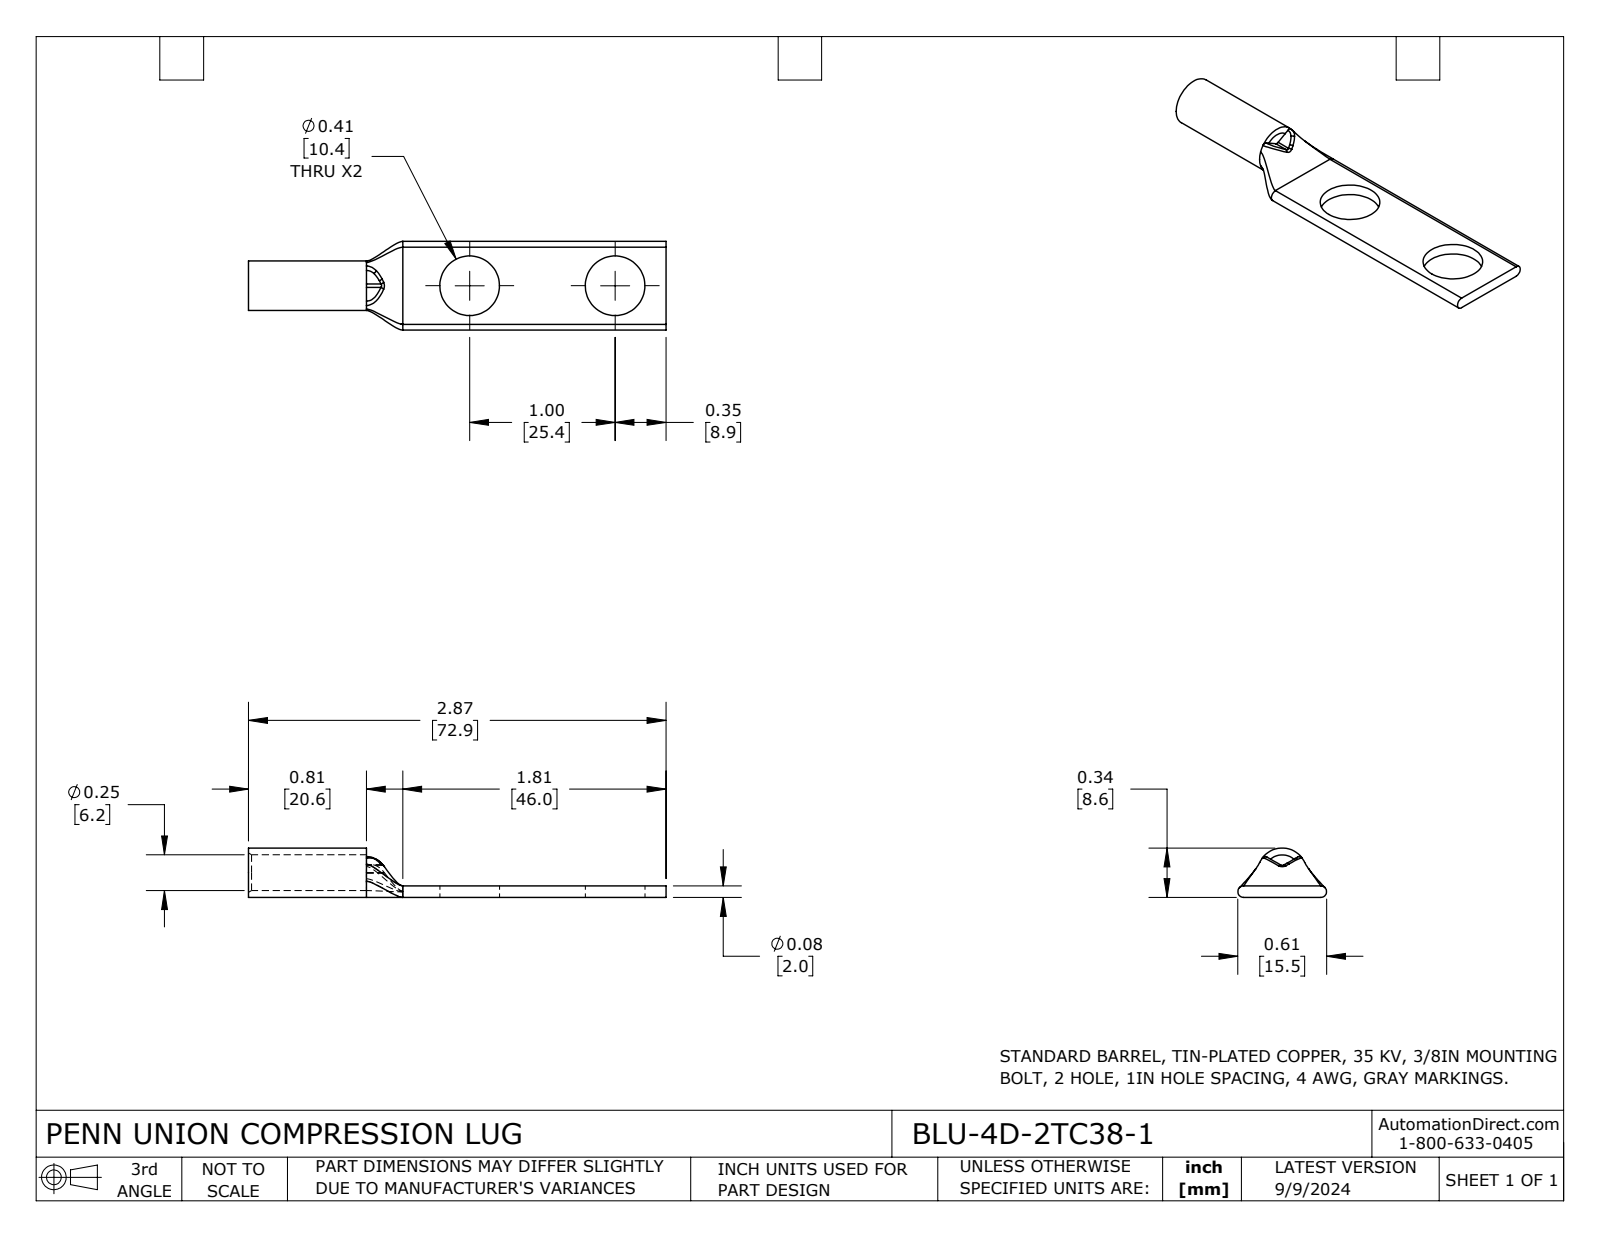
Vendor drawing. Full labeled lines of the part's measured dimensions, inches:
Part name (STEP PRODUCT): BLU-4D-2TC38-1
STEP written by: SolidWorks 2023 (CONFIG_CONTROL_DESIGN)
Units: inches
Bodies: 1 solid, 39 faces (11 planar, 13 cylindrical, 15 other)
Overall size (bounding box): 2.87 × 0.61 × 0.34
Volume: 0.11 in³ · Surface area: 4.233 in²
Round holes (diameter × count): ⌀0.41 ×2, ⌀0.246 ×1
Round bosses / shafts (diameter × count): ⌀0.34 ×1
Partial cylindrical surfaces — rounded edges, fillets, slot ends (radius × count): R0.024 ×2, R0.04 ×2
Main face-to-face distances: 0.08, 2.87, 0.81, 2.06, 0.047, 1.06, 0.25, 1.81
Hole centre spacings: 1
